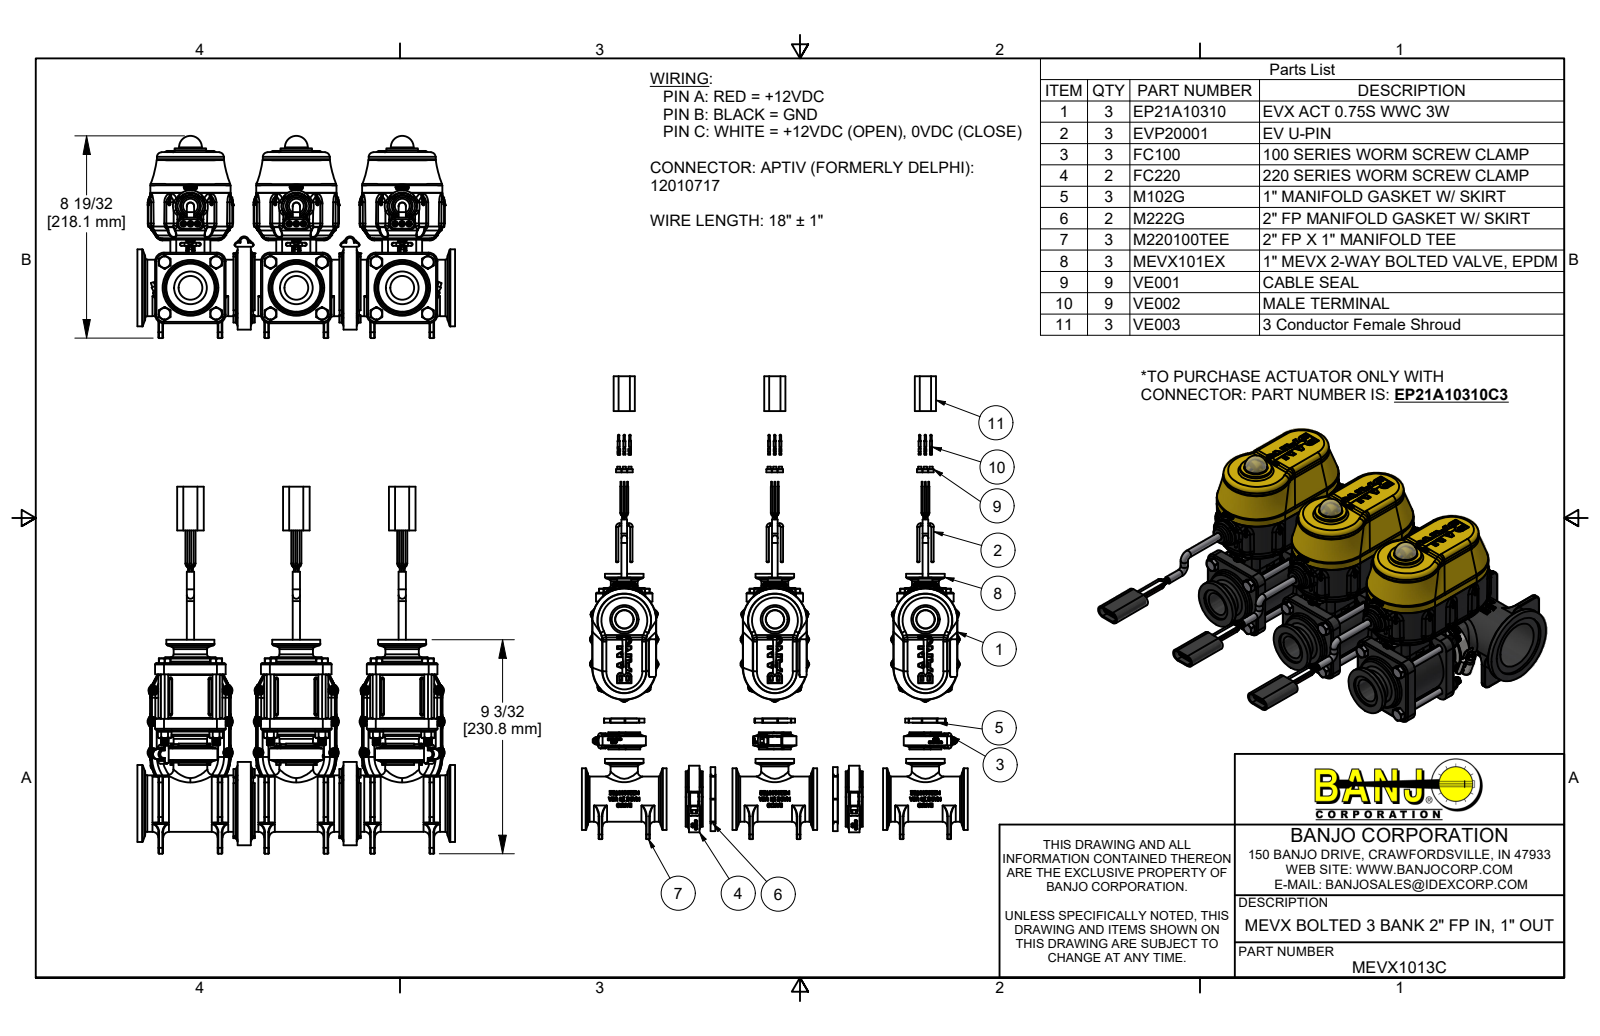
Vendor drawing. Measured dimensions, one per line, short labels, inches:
name: MEVX1013C; EP21A10310; EP10310; IRF4905 (+8 more)
written by: Autodesk Inventor 2021 (AUTOMOTIVE_DESIGN)
unit: in
bodies: 322 solids, 38605 faces (10114 planar, 11320 cylindrical, 17171 other)
size: 15.582 × 13.5 × 8.587
volume: 194.4 in³; area: 2 332 in²
holes: 33× ⌀0.095, 33× ⌀0.15, 21× ⌀0.08, 21× ⌀0.15, 17× ⌀0.25, 12× ⌀0.107, 12× ⌀0.126, 12× ⌀0.136, 12× ⌀0.148, 12× ⌀0.17, 12× ⌀0.252, 12× ⌀0.322
bosses: 180× ⌀0.268, 54× ⌀0.08, 51× ⌀0.25, 33× ⌀0.14, 33× ⌀0.108, 33× ⌀0.085, 18× ⌀0.058, 15× ⌀0.313
rounds: 540× R0.013, 435× R0.04, 277× R0.01, 247× R0.03, 242× R0.02, 143× R0.005, 114× R0.06, 89× R0.015
face distances: 4.5, 0.1, 2.565, 0.48, 9, 0.06, 0.211, 0.151, 0.125, 2.365
hole spacings: 4.5, 1.662, 1.891, 2.656, 2.715, 4.509, 4.581, 9
